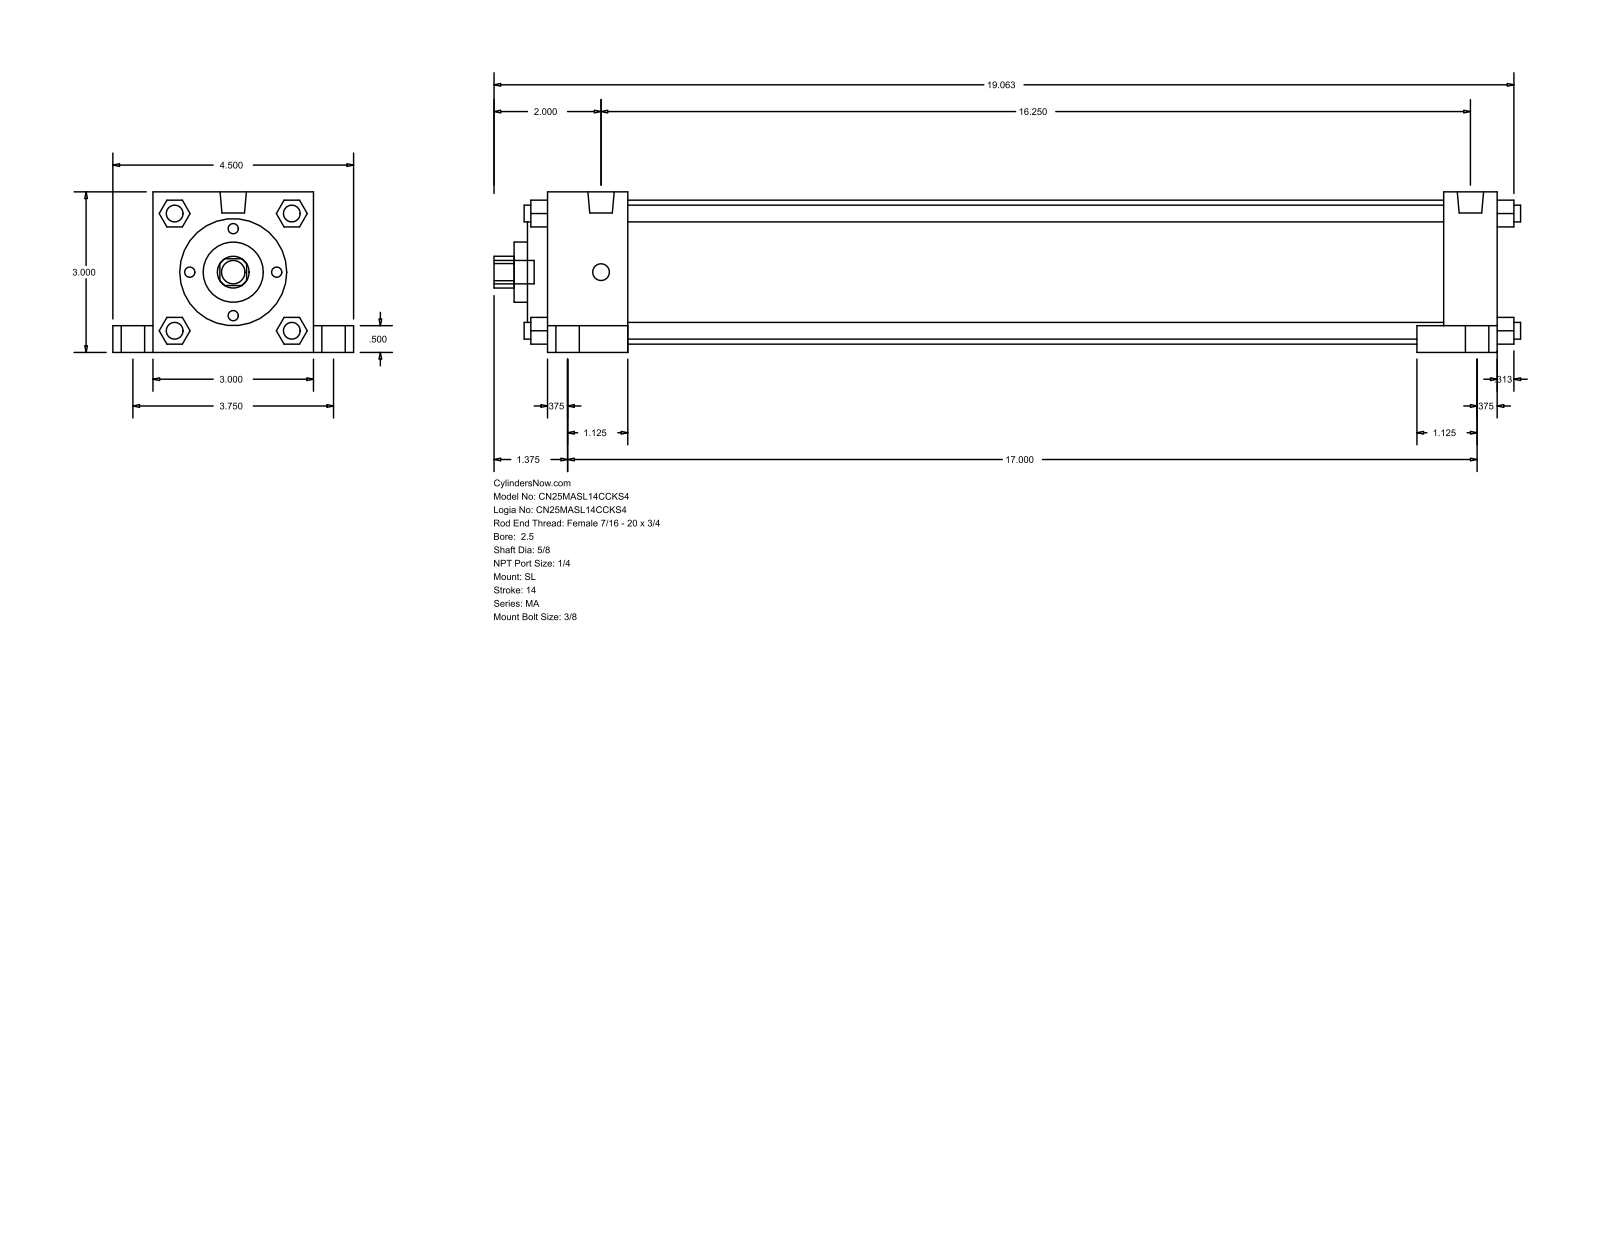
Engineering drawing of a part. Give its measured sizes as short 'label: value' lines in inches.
name: MA_SL__0250_0.625
written by: GSSL Pune (CONFIG_CONTROL_DESIGN)
unit: in
bodies: 0 solids, 150 faces (113 planar, 37 cylindrical, 0 other)
size: 19.187 × 4.5 × 3
holes: 1× ⌀0.625, 1× ⌀1.125, 1× ⌀2, 1× ⌀2.69
bosses: 8× ⌀0.313, 5× ⌀0.437, 4× ⌀0.687, 2× ⌀0.492
rounds: 1× R0.297
face distances: 3, 17.75, 0.5, 15.25, 1, 1.5, 16.25, 16.75, 0.75, 2.5
